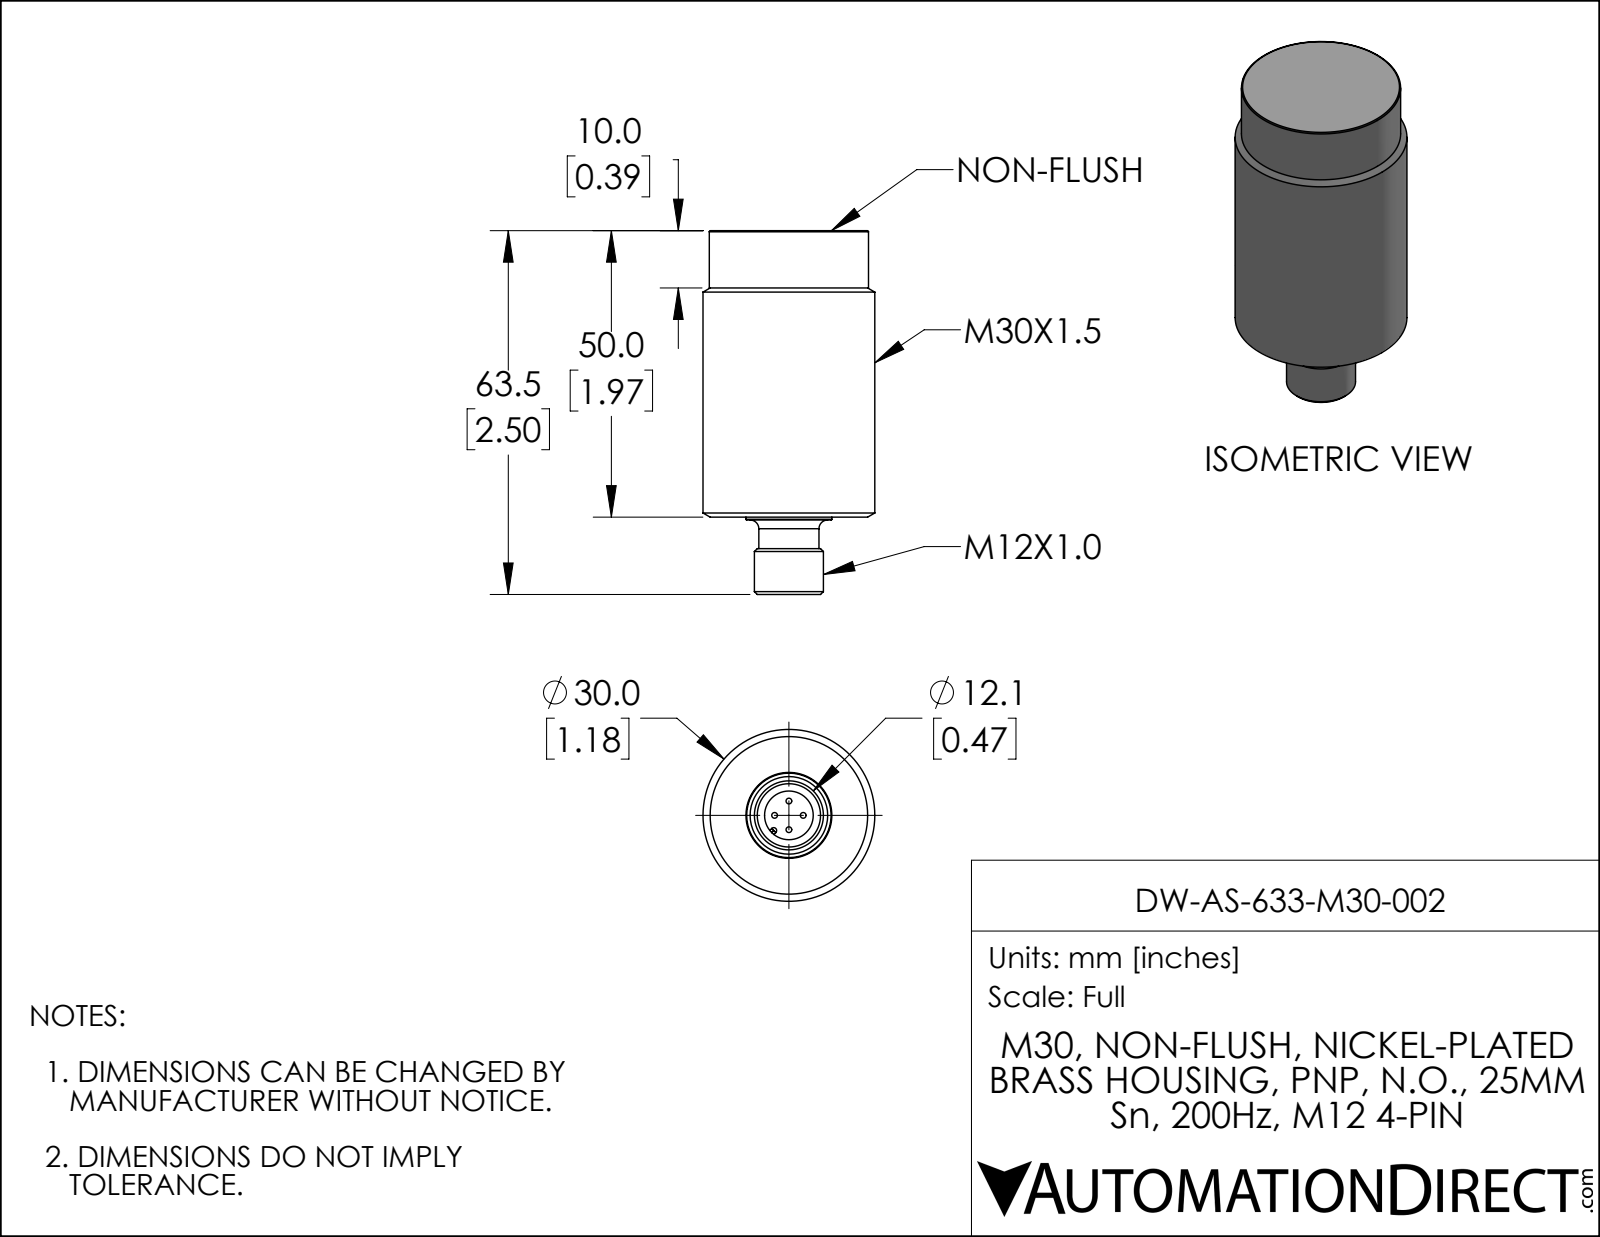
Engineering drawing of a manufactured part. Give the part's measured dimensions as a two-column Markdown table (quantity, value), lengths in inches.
| quantity | value |
| --- | --- |
| part name | DW-AS-631-M30-002 |
| STEP written by | SolidWorks 2019 (AUTOMOTIVE_DESIGN) |
| units | inches |
| bodies | 1 solid, 35 faces (10 planar, 13 cylindrical, 12 other) |
| overall size | 2.5 × 1.181 × 1.181 |
| volume | 2.153 in³ |
| surface area | 10.51 in² |
| round holes (diameter × count) | 0.335 × 1 |
| round bosses / shafts (diameter × count) | 0.039 × 4, 1.181 × 1, 1.094 × 1, 0.59 × 1, 0.474 × 1, 0.413 × 1 |
| partial cylindrical surfaces (radius × count) | 0.02 × 1, 0.02 × 1 |
| main face-to-face distances | 1.969, 2.185, 0.217, 2.5, 0.531, 0.315, 1.988, 0.02, 0.197, 0.512 |
